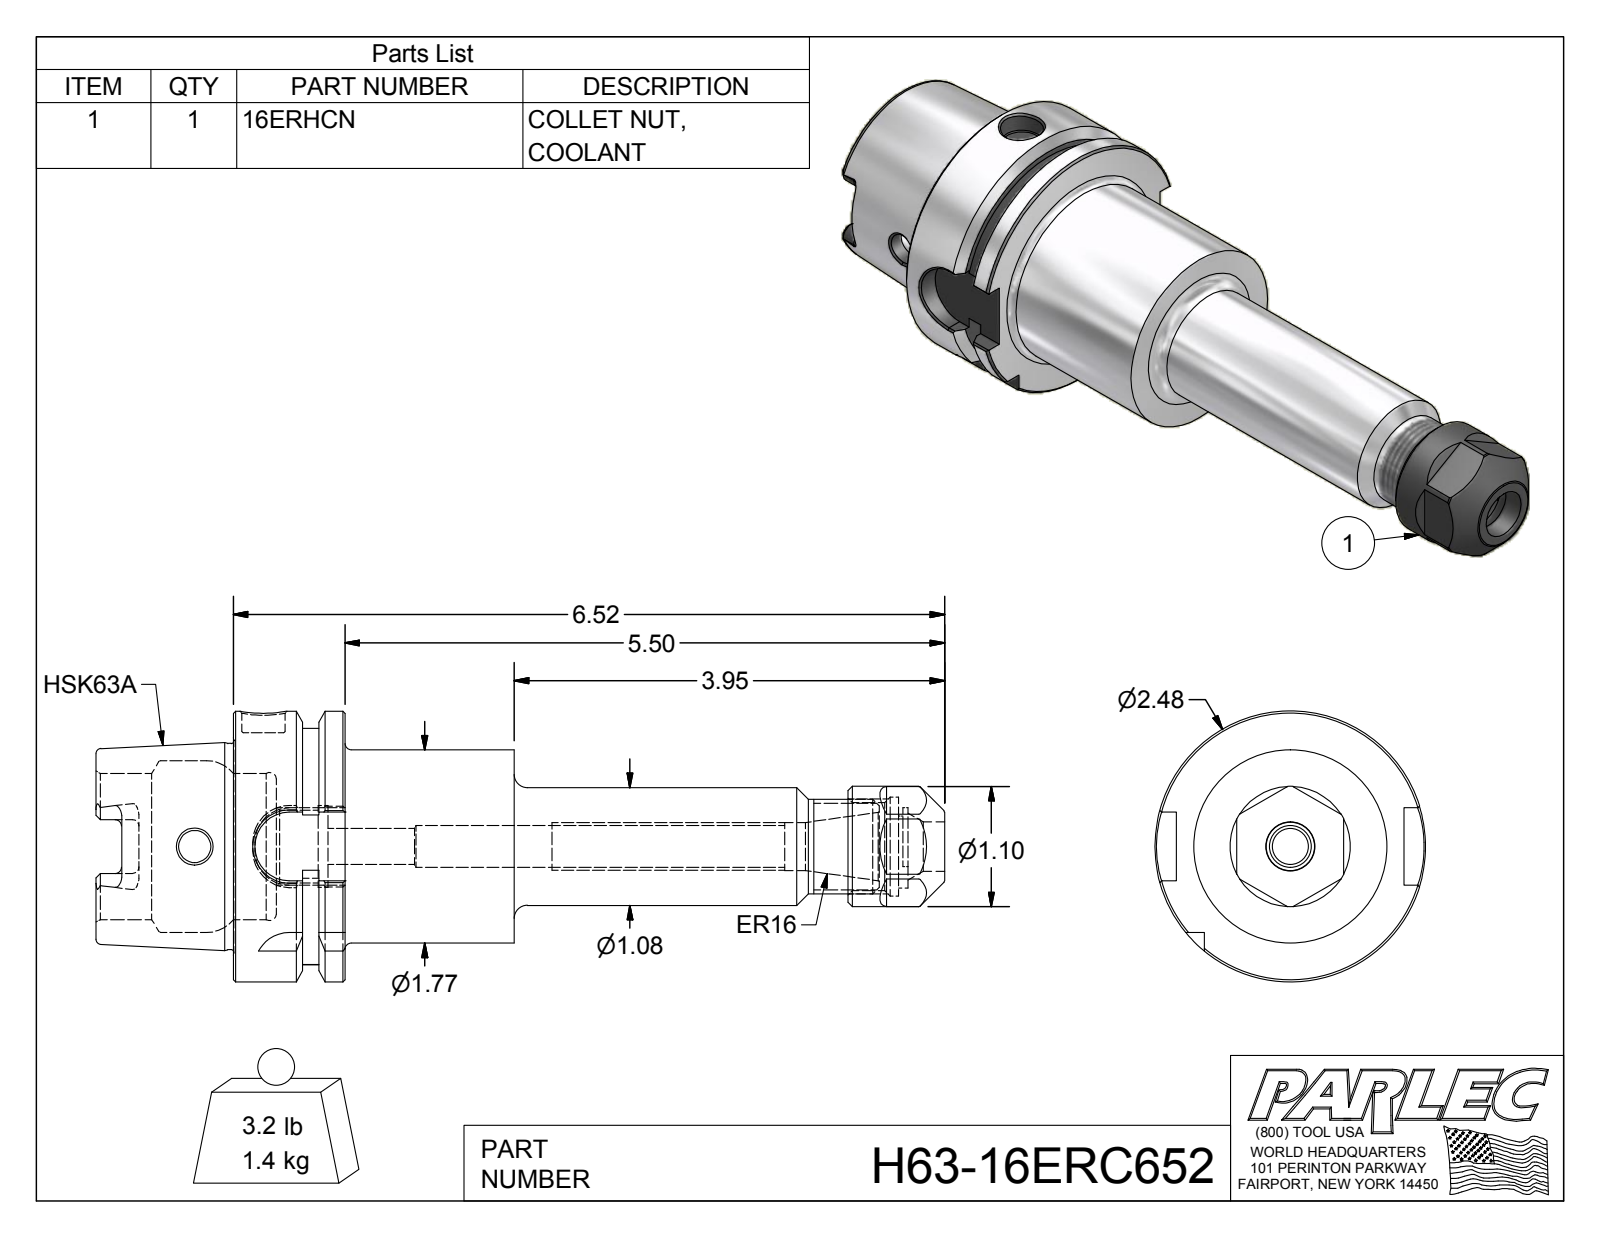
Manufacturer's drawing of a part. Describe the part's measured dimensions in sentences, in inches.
The part is named "H63-16ERC652; 16ERHCN; H63-16ER6-1". Its 3-D file was written by "Autodesk Inventor 2012 (AUTOMOTIVE_DESIGN)". It is 2 solids with 176 faces: 70 planar, 43 cylindrical and 63 other. Overall it measures 7.78 by 2.48 by 2.48 inches. Its volume is 11.35 cubic inches and its surface area 65.84 square inches. Round holes: 1 of diameter 0.295, 1 of diameter 0.331, 1 of diameter 0.383, 1 of diameter 0.394, 1 of diameter 0.44, 1 of diameter 0.453, 1 of diameter 0.661, 1 of diameter 0.666, 1 of diameter 0.749, 1 of diameter 0.807, 1 of diameter 0.906, 1 of diameter 1.339. Round bosses or shafts: 1 of diameter 2.48, 1 of diameter 1.891, 1 of diameter 1.77, 1 of diameter 1.102, 1 of diameter 1.08, 1 of diameter 0.866. Partial cylindrical surfaces (rounded edges, fillets, slot ends): 6 of radius 0.059, 4 of radius 0.113, 4 of radius 0.315, 1 of radius 0.354, 1 of radius 1.083. The main face-to-face distances are 1.024, 2.575, 1.552, 0.394, 0.63, 2.181, 1.26, 1.654, 2.283, 3.835. The hole center spacings are 0.051.
